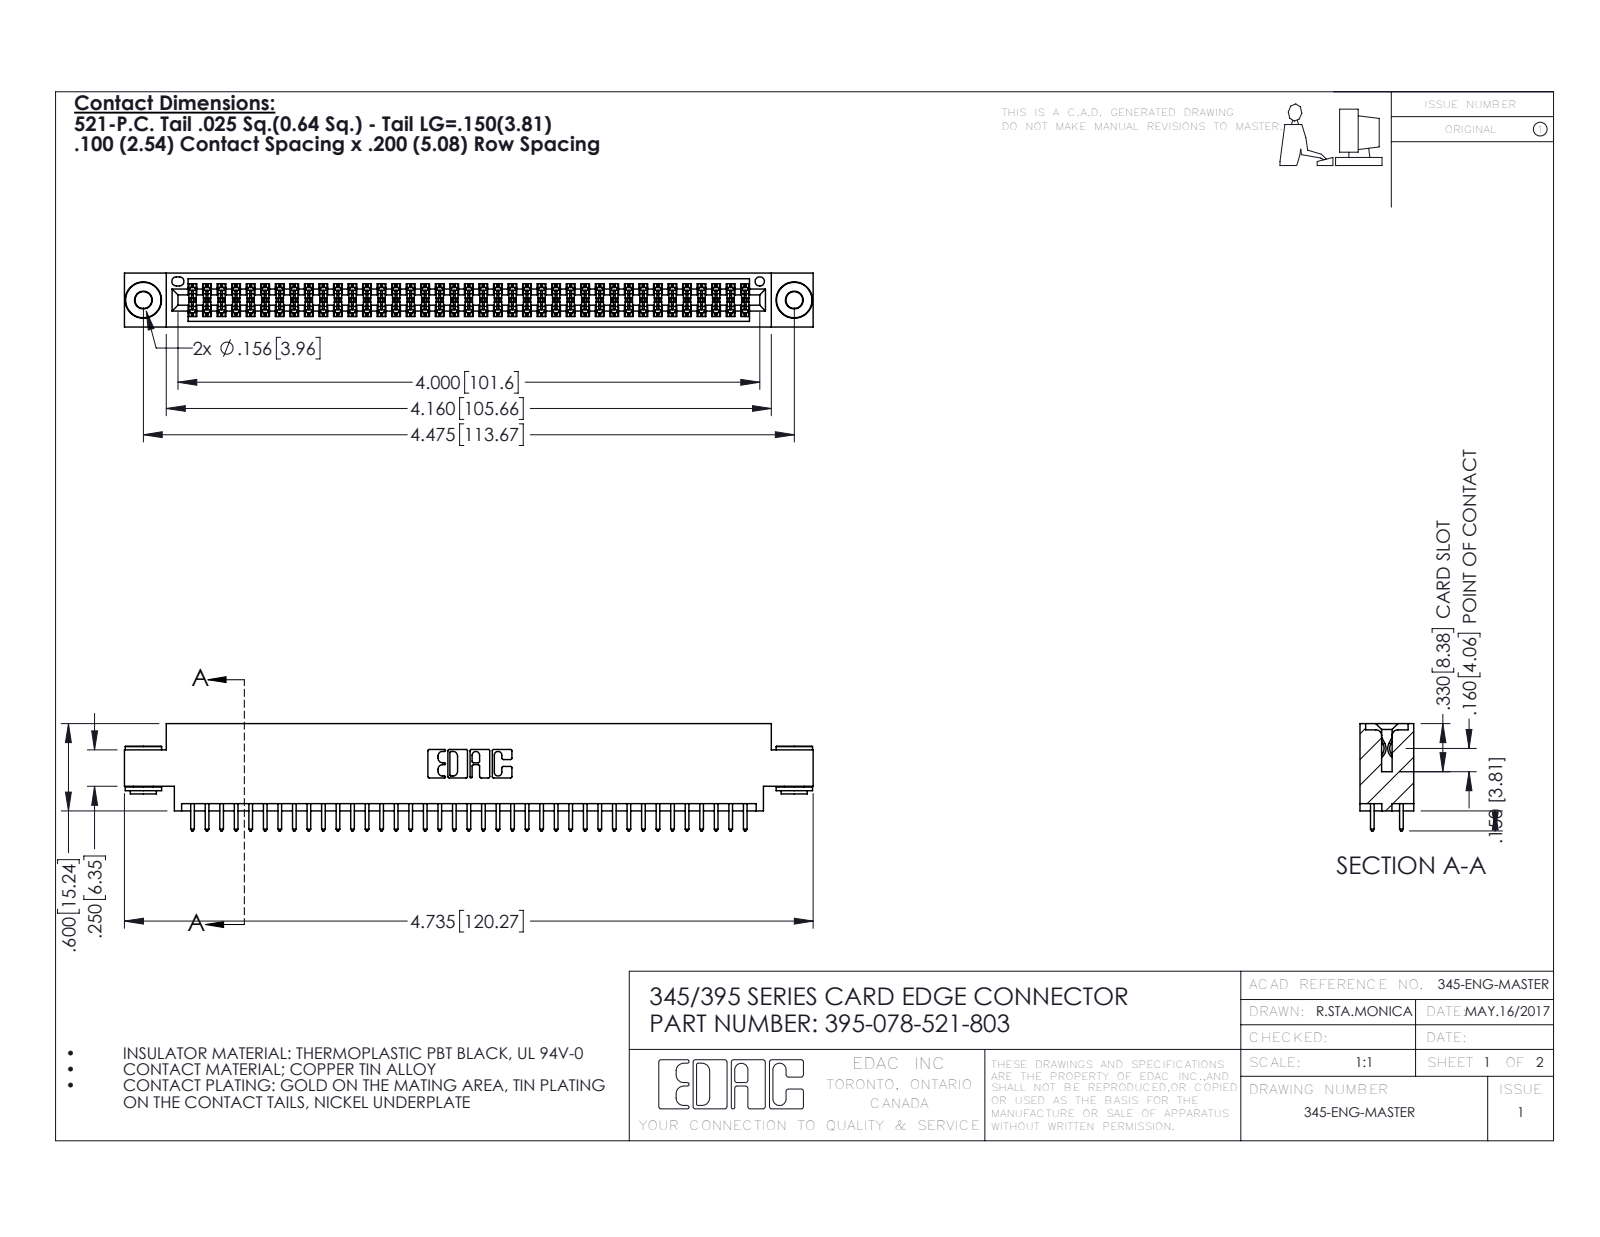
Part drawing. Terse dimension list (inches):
name: 345-292-001_345-293-121; 395-078-521-803; 345-250-002_345-250-002-102; 345 Part_0.170 Offset - 0.156 Dia-TH
written by: SolidWorks 2016 (CONFIG_CONTROL_DESIGN)
unit: in
bodies: 81 solids, 4068 faces (2668 planar, 1392 cylindrical, 8 other)
size: 4.735 × 0.737 × 0.37
volume: 0.704 in³; area: 26.54 in²
holes: 2× ⌀0.116, 2× ⌀0.156, 1× ⌀0.064
bosses: 2× ⌀0.25, 2× ⌀0.18, 2× ⌀0.136
rounds: 117× R0.006, 78× R0.01, 22× R0.01, 6× R0.007, 6× R0.031, 3× R0.026, 2× R0.014, 2× R0.019
face distances: 0.072, 0.298, 0.37, 0.2, 0.098, 0.272, 0.025, 0.225, 0.175, 0.149
hole spacings: 0.27, 4.239, 4.475
